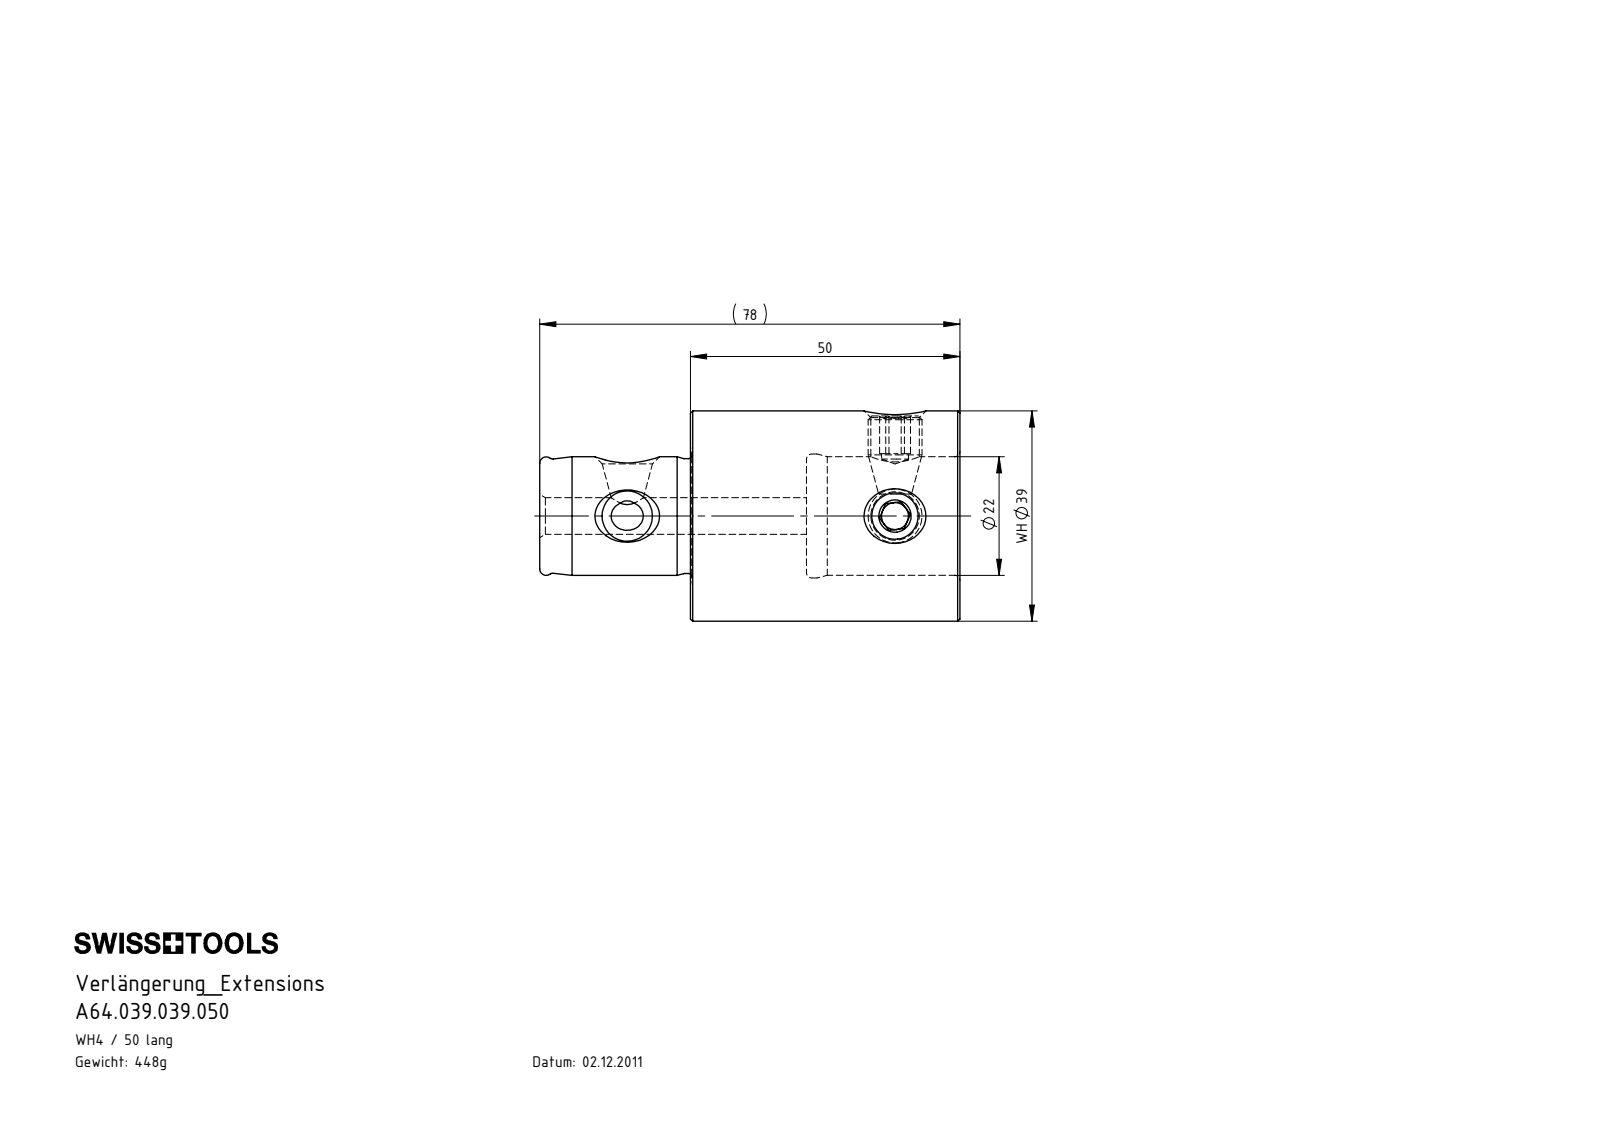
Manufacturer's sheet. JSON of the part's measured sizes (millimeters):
{"part_name": "WH4-ER1.001.015; WH4-WH4.001.050; WH4-WH4.001.050_A", "step_written_by": "SolidWorks 2015 (AUTOMOTIVE_DESIGN)", "units": "millimeters", "bodies": {"solids": 3, "faces": 94, "planar": 22, "cylindrical": 20, "other": 52}, "overall_size": [78, 39, 39], "volume_mm3": 57255, "surface_area_mm2": 14897, "round_holes": [[9, 2], [6.8, 1], [22, 1], [23, 1]], "round_bosses_or_shafts": [[10, 2], [39, 1], [21.3, 1]], "face_to_face_distances": [50, 21.5, 28.5, 28, 49.5, 78, 5, 14.5, 9.5]}
